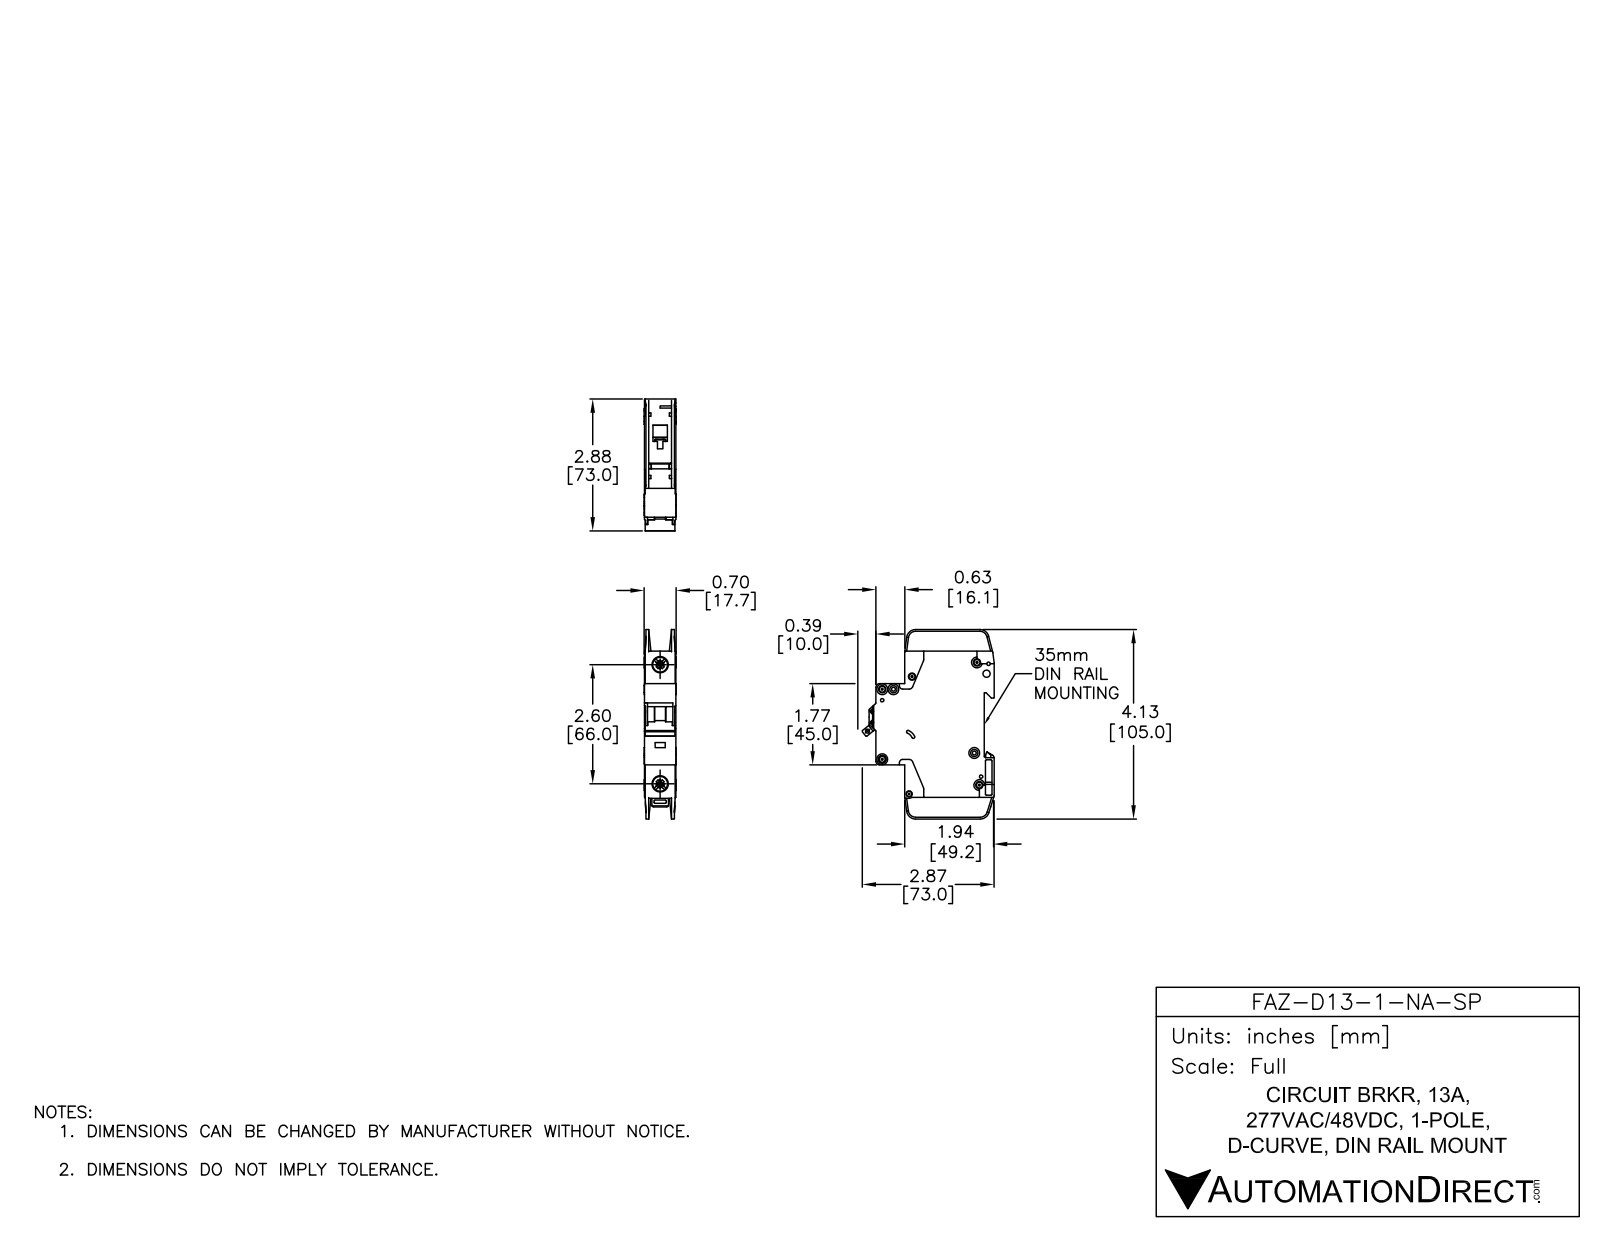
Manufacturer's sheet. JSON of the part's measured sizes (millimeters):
{"part_name": "FAZ-D13-1-NA-SP", "step_written_by": "SolidWorks 2014 (AUTOMOTIVE_DESIGN)", "units": "millimeters", "bodies": {"solids": 3, "faces": 784, "planar": 409, "cylindrical": 263, "other": 112}, "overall_size": [105, 73.04, 17.7], "volume_mm3": 77695, "surface_area_mm2": 24740, "round_holes": [[3.6, 7], [1.09, 2], [1.5, 2], [4, 2], [7.15, 2], [8.2, 2], [1.9, 1], [2.15, 1], [2.2, 1], [2.55, 1], [3.3, 1], [3.4, 1]], "round_bosses_or_shafts": [[6, 7], [2.5, 1]], "partial_cylinders_radius": [[0.25, 29], [0.5, 18], [1, 10], [2, 10], [5, 5], [4, 4], [1.8, 3], [0.2, 2]], "face_to_face_distances": [17.5, 15.05, 0.7, 2.45, 1.75, 15.75, 13.3, 14, 12.6, 2], "hole_center_spacings": [6.2, 5.19, 6.1, 8.19, 8.56, 8.7, 11.11, 12.45]}
